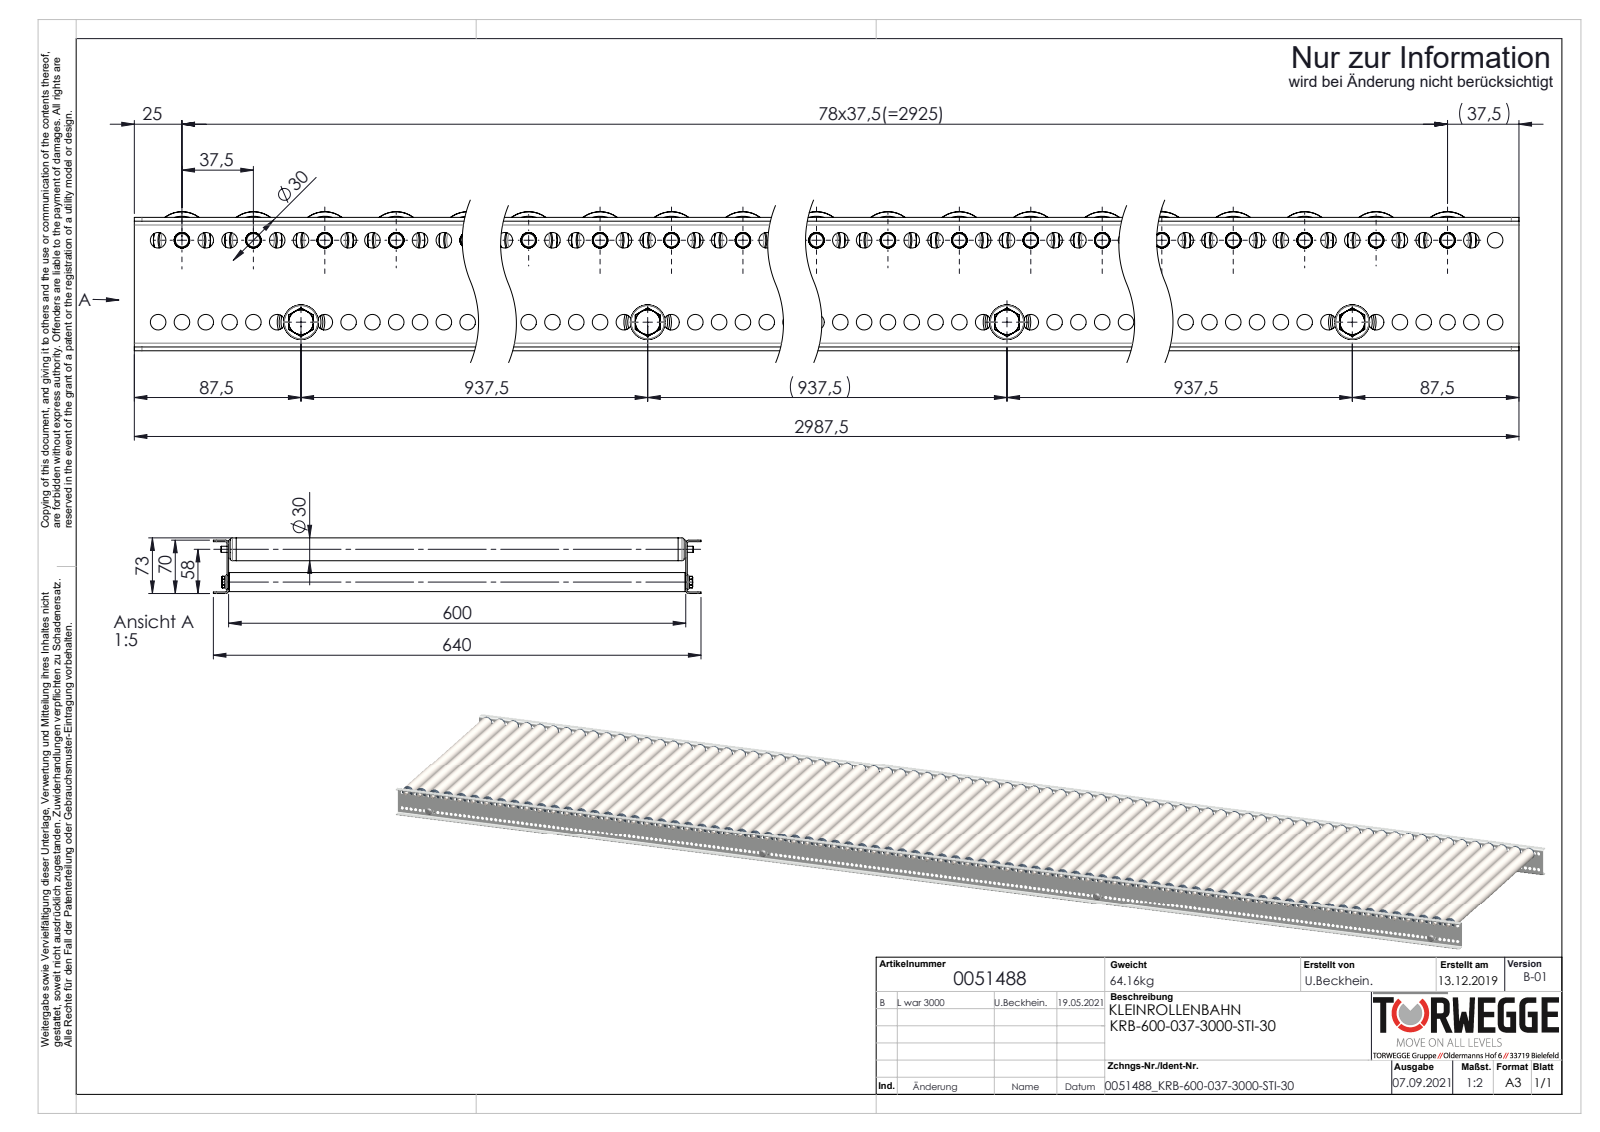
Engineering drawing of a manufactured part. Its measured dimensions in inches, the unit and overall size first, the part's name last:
Units: inches
Overall size (bounding box): 117.618 × 25.197 × 2.874
Round holes (diameter × count): ⌀0.323 ×476, ⌀0.315 ×79, ⌀0.319 ×79, ⌀0.913 ×79, ⌀0.992 ×79, ⌀1.063 ×79, ⌀0.268 ×4, ⌀0.827 ×4
Round bosses / shafts (diameter × count): ⌀1.181 ×79, ⌀1.177 ×79, ⌀1.067 ×79, ⌀1.055 ×79, ⌀0.945 ×79, ⌀0.551 ×79, ⌀0.984 ×4, ⌀0.315 ×4
Partial cylindrical surfaces — rounded edges, fillets, slot ends (radius × count): R0.199 ×79, R0.157 ×8, R0.079 ×4
Main face-to-face distances: 0.079, 23.701, 23.622, 2.677, 23.78, 2.756, 2.598, 0.394, 23.228, 0.787
Hole centre spacings: 0.492, 0.984, 1.476, 1.969, 2.461, 2.953, 3.445, 3.937
Volume: 622.4 in³ · Surface area: 18 850 in²
Bodies: 496 solids, 20898 faces (6524 planar, 8320 cylindrical, 6054 other)
Part name (STEP PRODUCT): 0042503_Typ-KUT50-30x1,5-A8; 0024176_Passscheibe_DIN988_8x14x1; 0039778-Achse-ST-Ø08-KFG_AL620-G-FA; 0039768_Tragrollenrohr-Ø30x1,5STI_KFG_0039768_L=580 (+6 more)
STEP written by: SolidWorks 2020 (AUTOMOTIVE_DESIGN)
